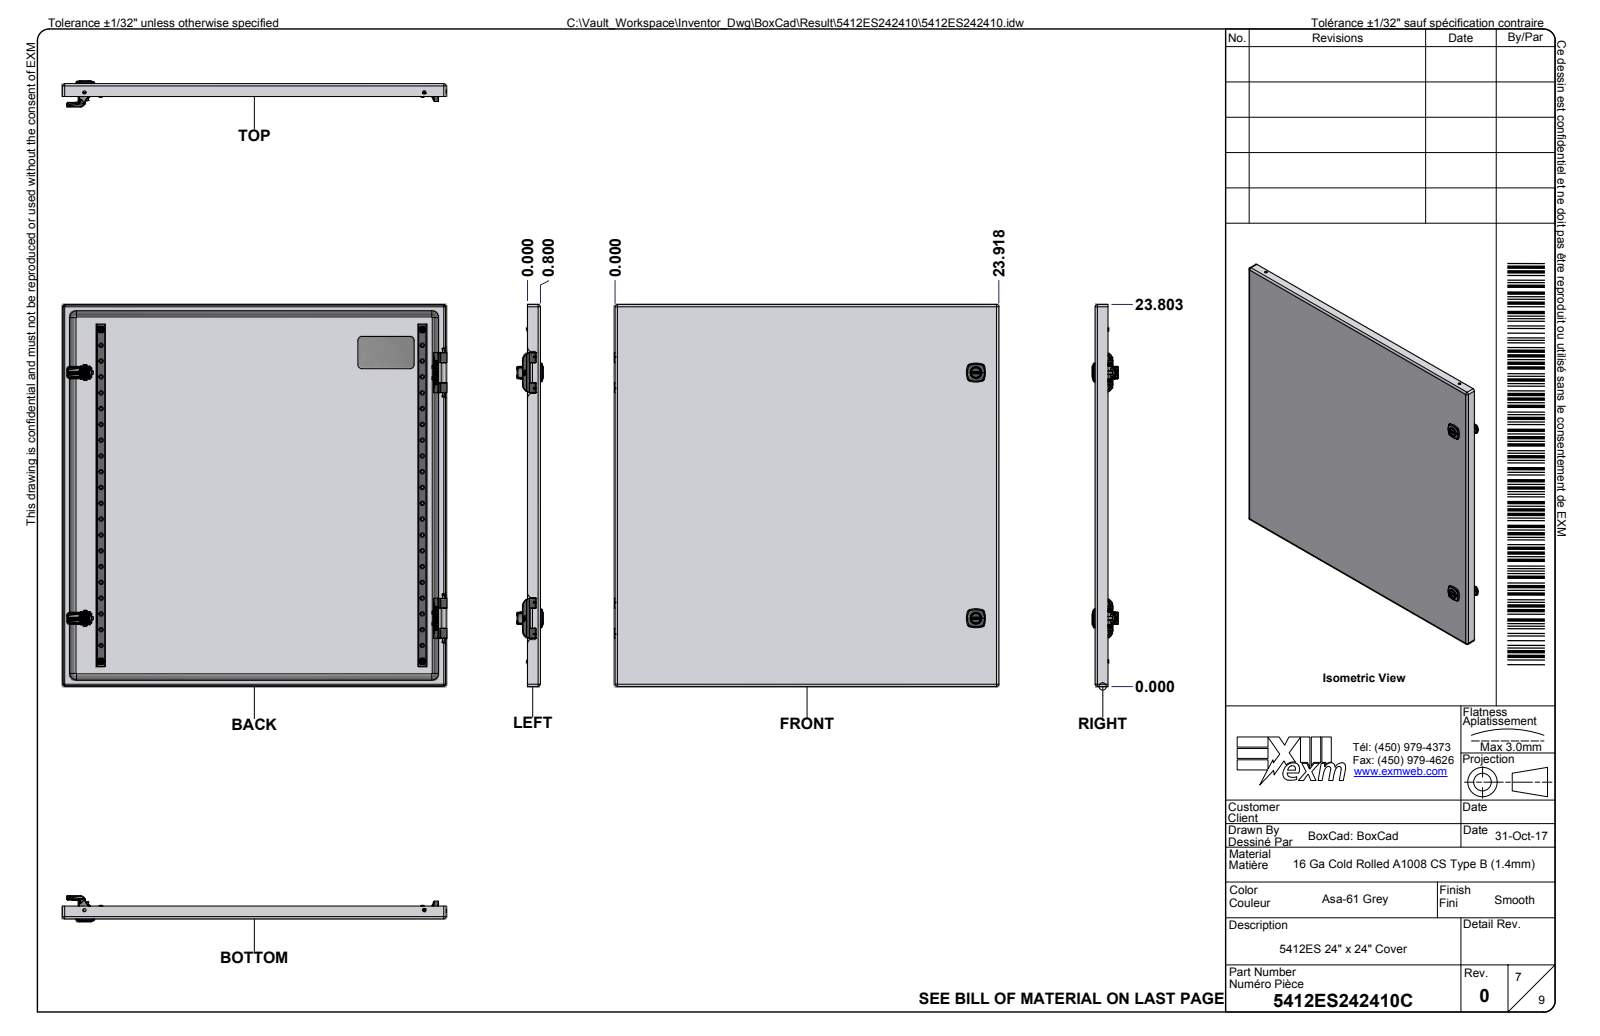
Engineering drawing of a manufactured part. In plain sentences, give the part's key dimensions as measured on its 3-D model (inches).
The part is named "5412ES242410; 5412ES242410B; 5412ES242410B-P; STK-Q-16005 (+8 more)". Its 3-D file was written by "Autodesk Inventor 2024 (AUTOMOTIVE_DESIGN)". It is 64 solids with 10070 faces: 3049 planar, 2555 cylindrical and 4466 other. Overall it measures 24.003 by 24 by 11.31 inches. Its volume is 191.9 cubic inches and its surface area 6 078 square inches. Round holes: 40 of diameter 0.165, 9 of diameter 0.03, 8 of diameter 0.043, 8 of diameter 0.201, 8 of diameter 0.315, 6 of diameter 0.311, 4 of diameter 0.178, 4 of diameter 0.197, 4 of diameter 0.268, 4 of diameter 0.27, 4 of diameter 0.29, 4 of diameter 0.39. Round bosses or shafts: 40 of diameter 0.237, 9 of diameter 0.232, 9 of diameter 0.03, 8 of diameter 0.039, 4 of diameter 0.717, 4 of diameter 0.374, 4 of diameter 0.311, 4 of diameter 0.262. Partial cylindrical surfaces (rounded edges, fillets, slot ends): 263 of radius 0.02, 139 of radius 0.01, 109 of radius 0.039, 94 of radius 0.008, 50 of radius 0.012, 32 of radius 0.031, 30 of radius 0.016, 24 of radius 0.084. The main face-to-face distances are 0.053, 11.081, 23.947, 11.028, 11.135, 0.927, 0.874, 10.154, 10.207, 1.032. The hole center spacings are 1.969, 0.984, 2.953, 3.937, 21.405, 15.303, 4.921, 5.906.
